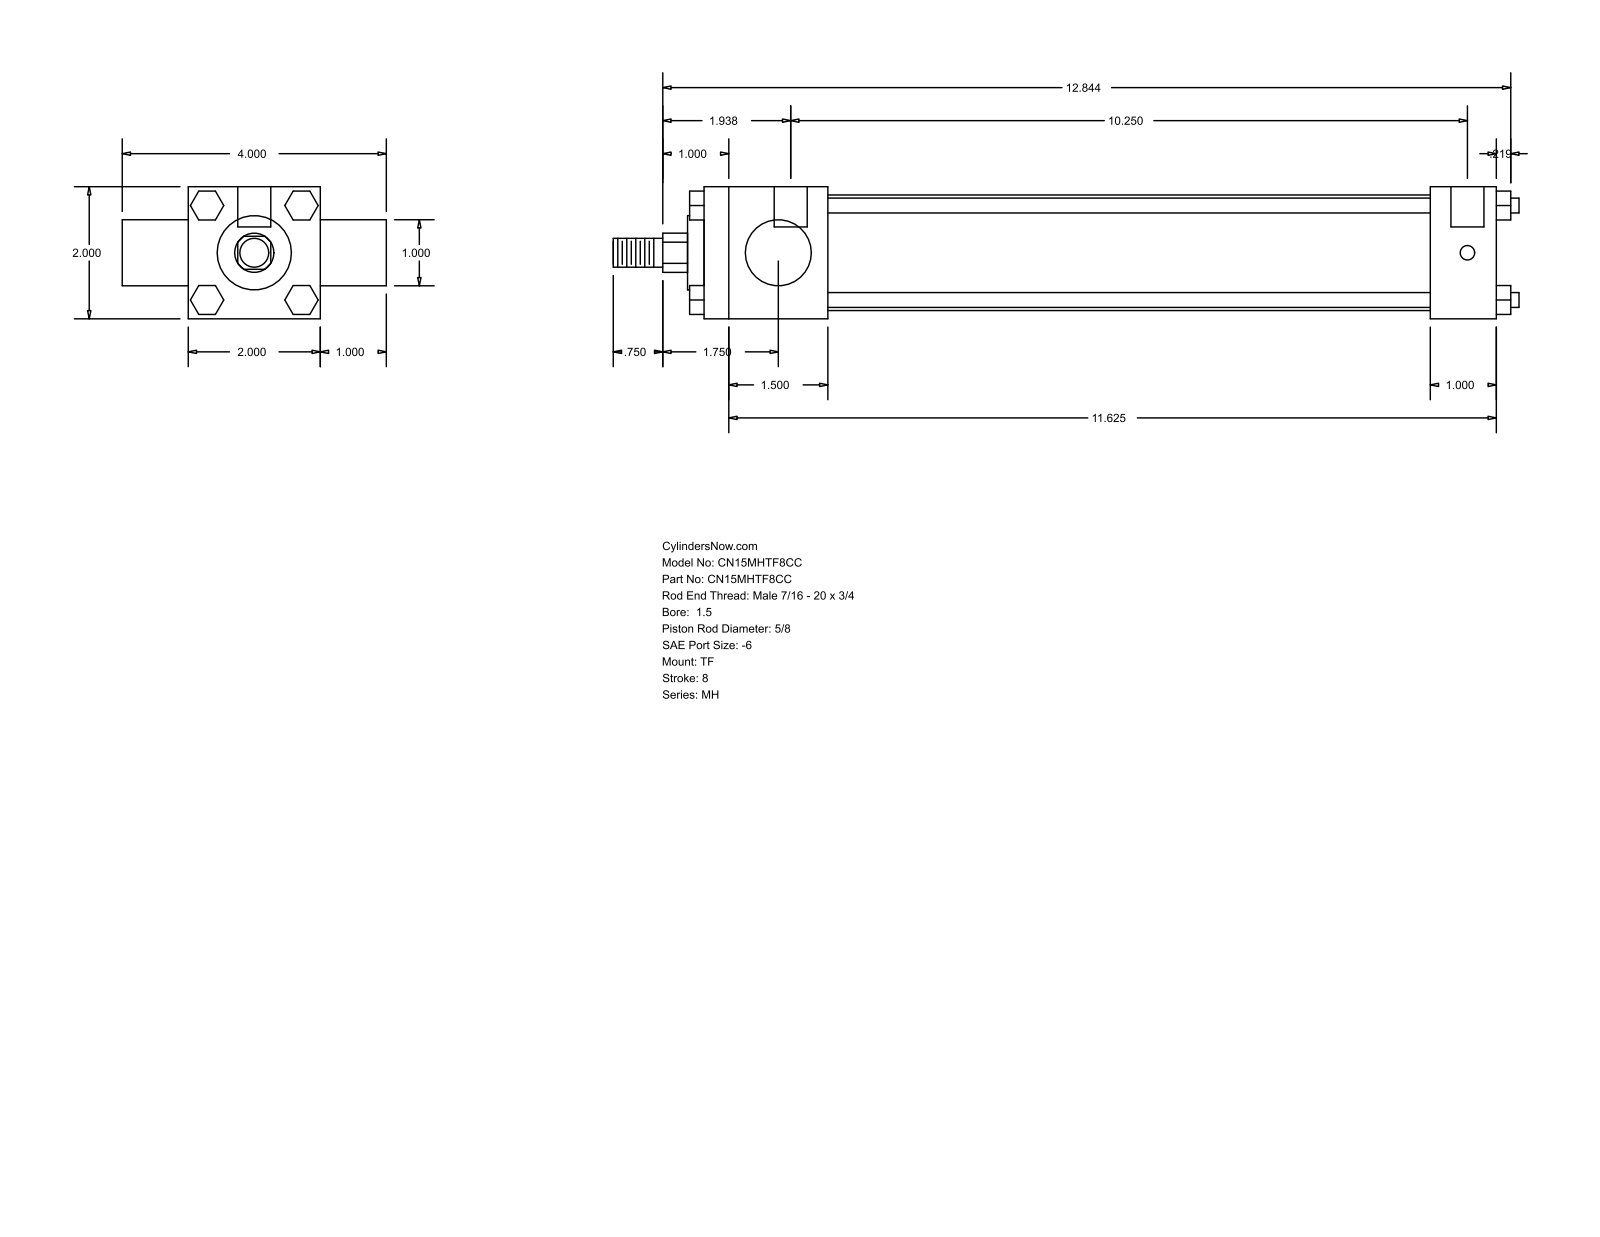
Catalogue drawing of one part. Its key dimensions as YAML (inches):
part_name: "MH_TF__0150_0.625"
step_written_by: "GSSL Pune (CONFIG_CONTROL_DESIGN)"
units: inches
bodies: {solids: 0, faces: 120, planar: 92, cylindrical: 28, other: 0}
overall_size: [13.719, 4, 2]
round_holes:
  - {diameter: 0.219, count: 3}
  - {diameter: 0.5, count: 2}
round_bosses_or_shafts:
  - {diameter: 0.225, count: 4}
  - {diameter: 1.75, count: 1}
  - {diameter: 1.125, count: 1}
  - {diameter: 1, count: 1}
  - {diameter: 0.625, count: 1}
  - {diameter: 0.437, count: 1}
partial_cylinders:
  - {radius: 0.297, count: 1}
face_to_face_distances: [2, 12, 1, 3, 1.875, 10.125, 11, 9.125, 1, 0.437]
hole_center_spacings: [0.125, 10.25, 10.375]
